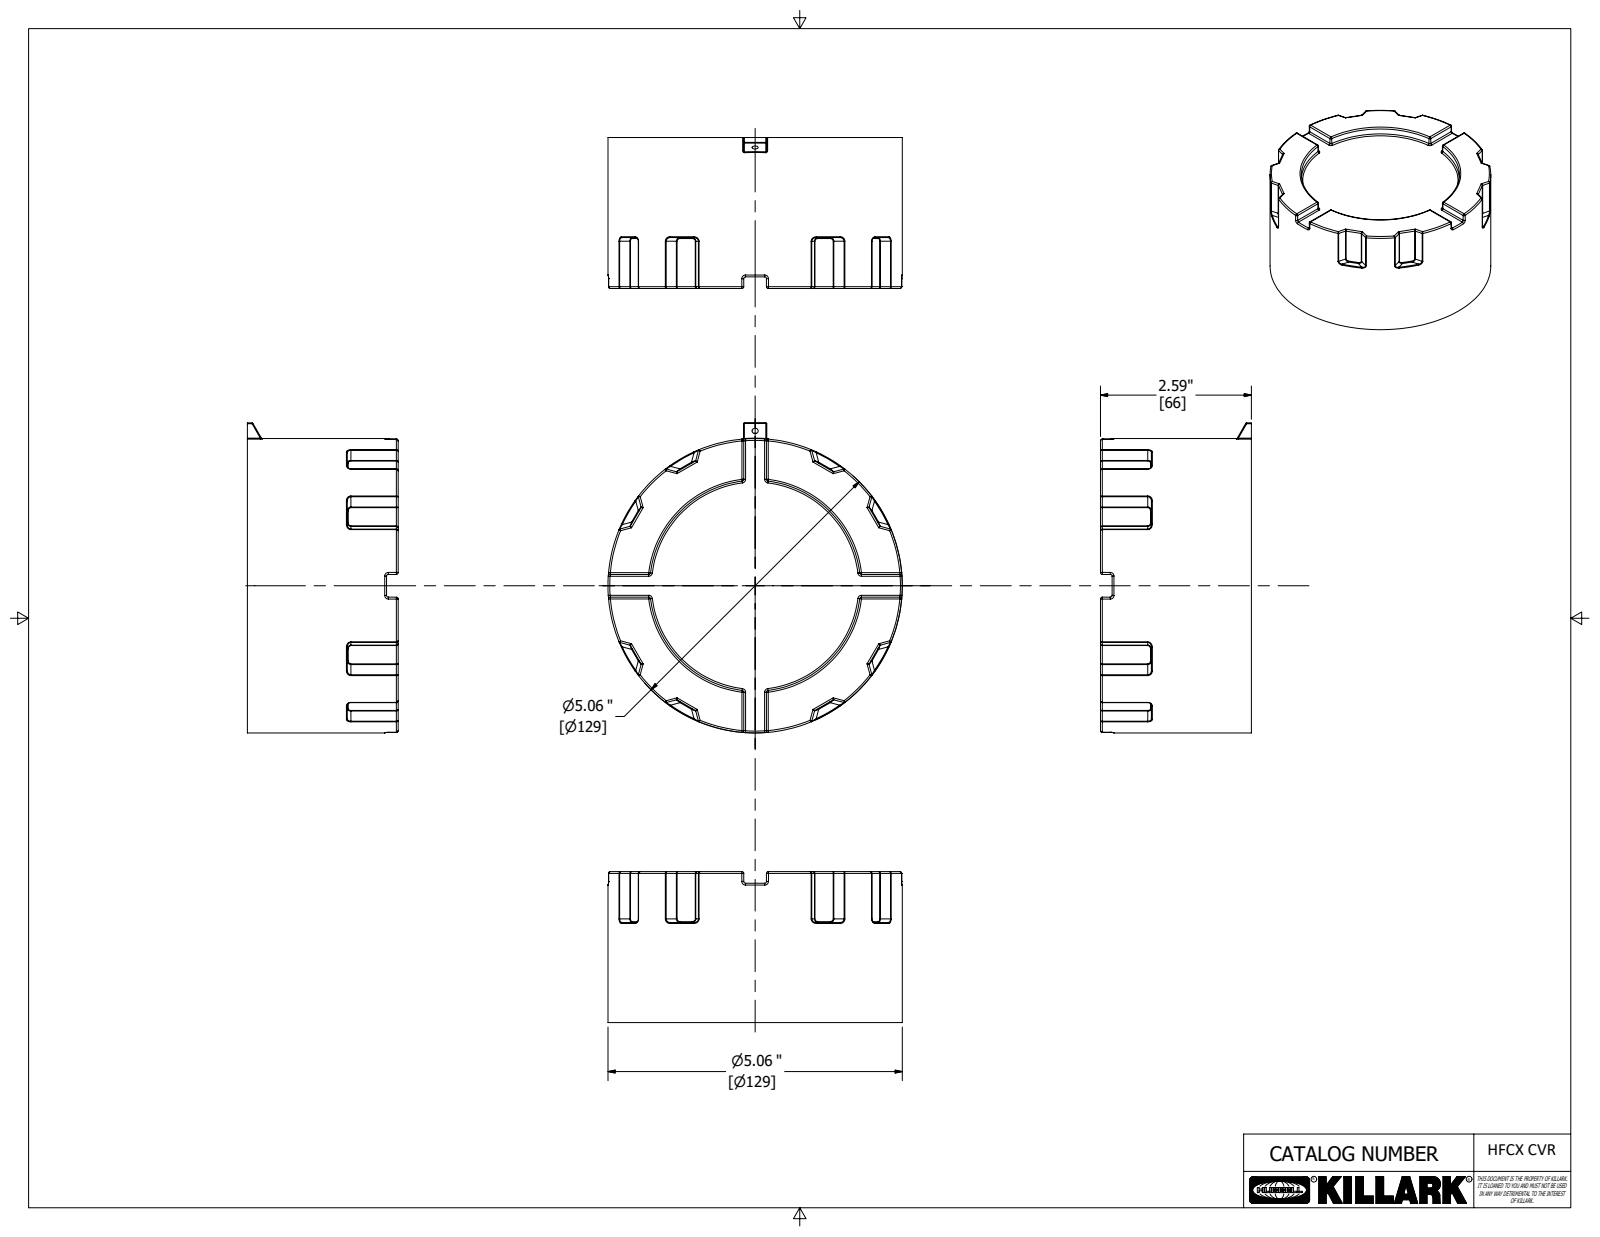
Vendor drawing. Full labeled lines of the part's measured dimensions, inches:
Part name (STEP PRODUCT): 51637ABAM for web
STEP written by: Autodesk Inventor 2020 (AUTOMOTIVE_DESIGN)
Units: inches
Bodies: 1 solid, 319 faces (51 planar, 128 cylindrical, 140 other)
Overall size (bounding box): 5.33 × 5.06 × 2.594
Volume: 17.86 in³ · Surface area: 110.2 in²
Round holes (diameter × count): ⌀0.104 ×1, ⌀3.624 ×1, ⌀4.2 ×1, ⌀4.39 ×1, ⌀4.86 ×1
Round bosses / shafts (diameter × count): ⌀5.06 ×1
Partial cylindrical surfaces — rounded edges, fillets, slot ends (radius × count): R0.031 ×48, R0.016 ×47, R0.062 ×16
Main face-to-face distances: 0.25, 0.45, 0.2, 2.144, 2.394, 2.594, 4.74, 3.087, 3.087, 3.087
